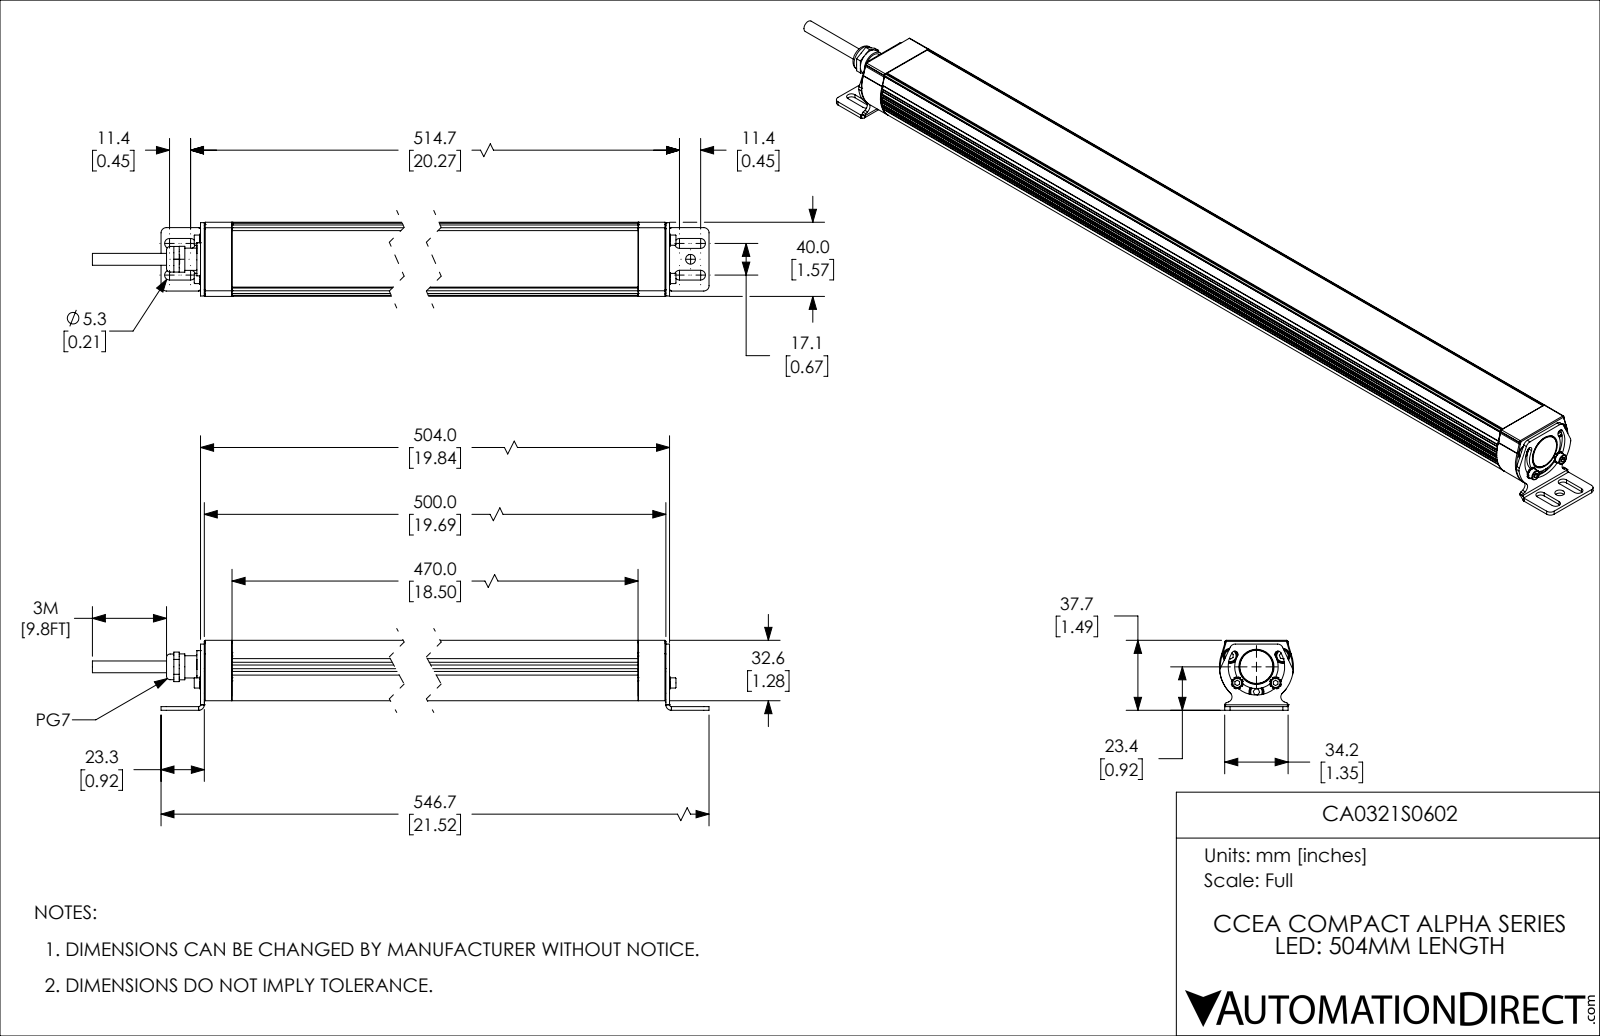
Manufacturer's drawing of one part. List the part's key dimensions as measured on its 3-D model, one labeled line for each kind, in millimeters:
Part name (STEP PRODUCT): CA0321S0602
STEP written by: SolidWorks 2021 (CONFIG_CONTROL_DESIGN)
Units: millimetres
Bodies: 22 solids, 1182 faces (392 planar, 577 cylindrical, 213 other)
Overall size (bounding box): 583.73 × 40 × 37.73
Volume: 273 279 mm³ · Surface area: 203 692 mm²
Round holes (diameter × count): ⌀2 ×4, ⌀3.3 ×3, ⌀4.5 ×3, ⌀7.5 ×3, ⌀2.5 ×2, ⌀3.2 ×2, ⌀5.3 ×2, ⌀8.5 ×1, ⌀11.5 ×1, ⌀12 ×1, ⌀14 ×1, ⌀19 ×1
Round bosses / shafts (diameter × count): ⌀1 ×4, ⌀7 ×3, ⌀4 ×3, ⌀5.5 ×2, ⌀3 ×2, ⌀18.3 ×1, ⌀15 ×1, ⌀13.86 ×1
Partial cylindrical surfaces — rounded edges, fillets, slot ends (radius × count): R0.25 ×56, R1 ×22, R3 ×22, R2.65 ×8, R2.85 ×6, R5.5 ×6, R1.5 ×4, R0.3 ×2
Main face-to-face distances: 2, 4.01, 0.5, 4.51, 27.98, 28.48, 32.49, 2.5, 25.98, 6.51
Hole centre spacings: 13.5, 1, 4.68, 5.63, 11.41, 13.07, 13.16, 15.09
